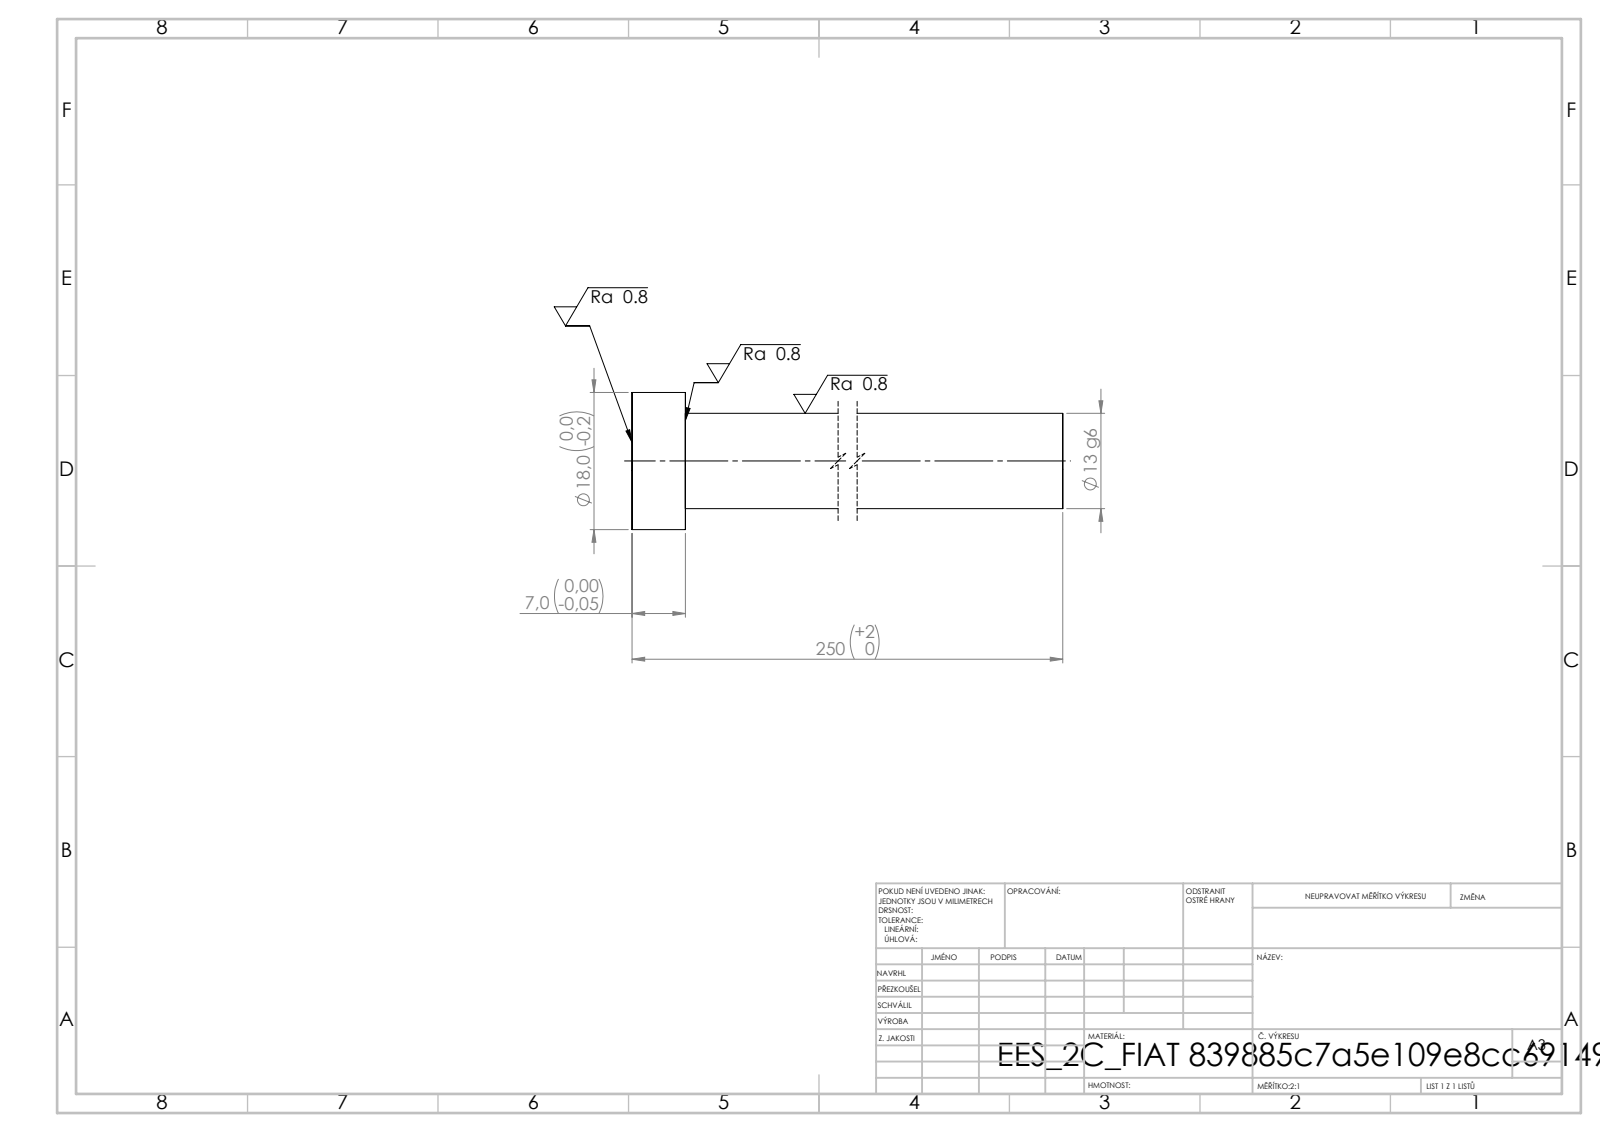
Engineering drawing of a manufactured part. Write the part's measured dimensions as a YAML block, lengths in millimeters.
step_written_by: "SolidWorks 2019 (CONFIG_CONTROL_DESIGN)"
units: millimeters
bodies: {solids: 1, faces: 7, planar: 3, cylindrical: 4, other: 0}
overall_size: [250, 18, 18]
volume: 31602
surface_area: 10447
round_bosses_or_shafts:
  - {diameter: 18, count: 1}
  - {diameter: 12.5, count: 1}
face_to_face_distances: [7, 250, 243]
